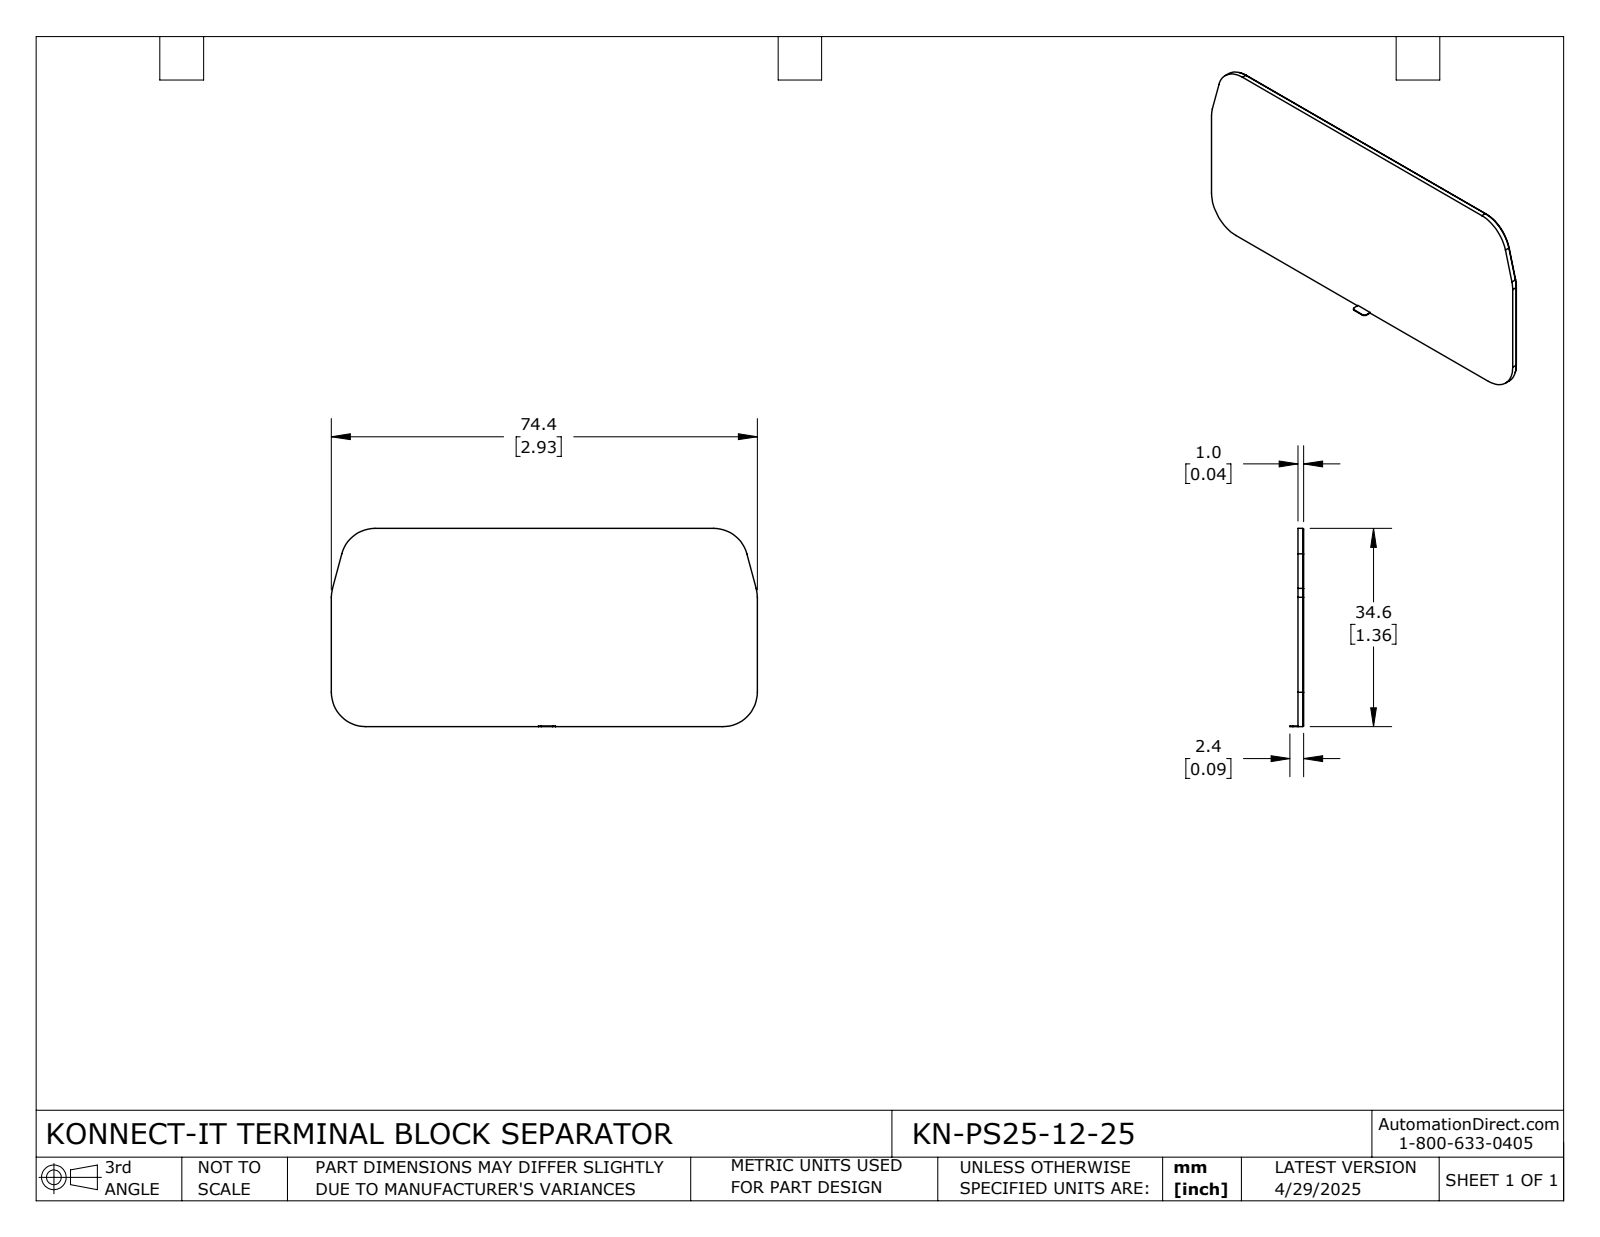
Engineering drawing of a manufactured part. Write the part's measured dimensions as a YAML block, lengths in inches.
part_name: "KN-PS25-12-25"
step_written_by: "SolidWorks 2024 (CONFIG_CONTROL_DESIGN)"
units: inches
bodies: {solids: 1, faces: 33, planar: 19, cylindrical: 14, other: 0}
overall_size: [2.928, 1.363, 0.094]
volume: 0.153
surface_area: 8.131
partial_cylinders:
  - {radius: 0.232, count: 6}
  - {radius: 0.236, count: 6}
  - {radius: 0.02, count: 2}
face_to_face_distances: [0.039, 1.363, 1.359, 0.033, 2.928, 1.355, 2.924, 2.92, 0.055, 0.089]
